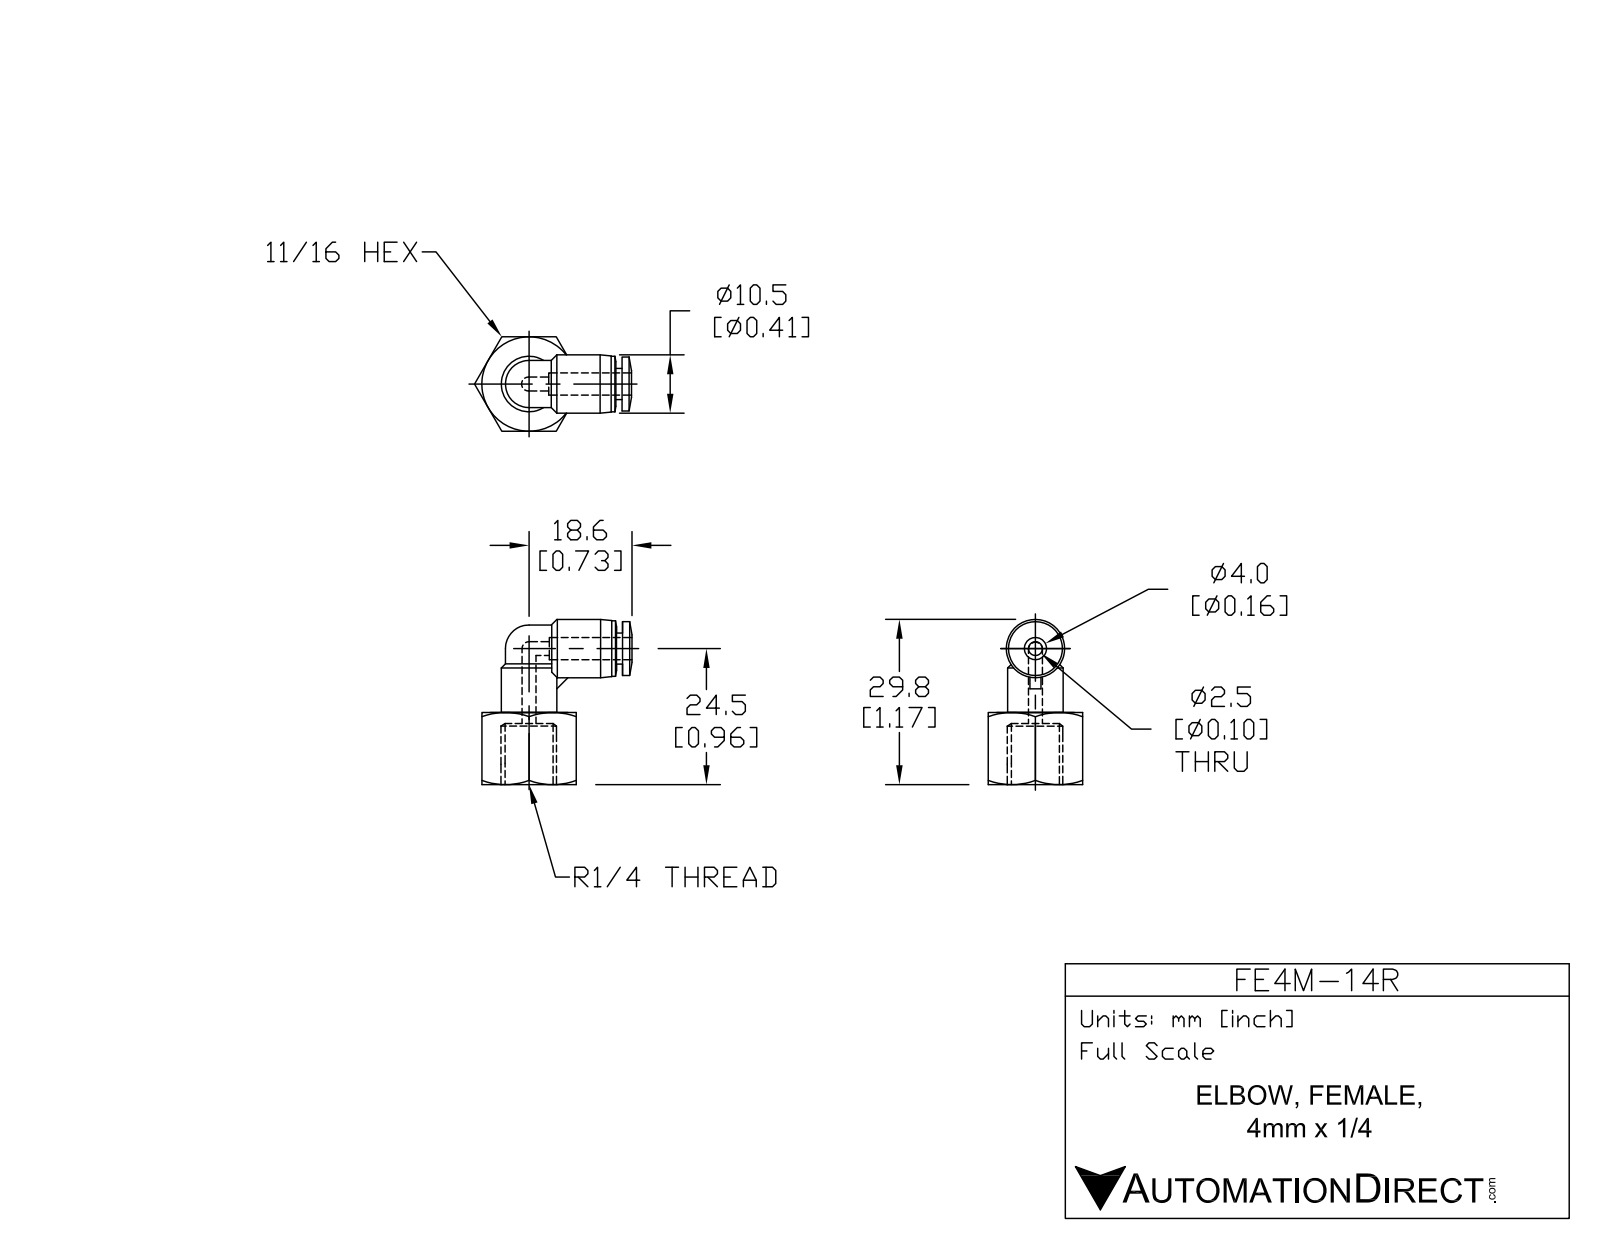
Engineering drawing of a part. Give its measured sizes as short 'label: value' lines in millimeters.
name: FE4M-14R
written by: SolidWorks 2015 (AUTOMOTIVE_DESIGN)
unit: mm
bodies: 1 solid, 67 faces (17 planar, 19 cylindrical, 31 other)
size: 29.7 × 28.3 × 17
volume: 3 640 mm³; area: 2 997 mm²
holes: 2× ⌀3, 1× ⌀4.3
bosses: 2× ⌀10, 1× ⌀10.5, 1× ⌀9.7, 1× ⌀5.6
rounds: 2× R4.2
face distances: 17, 2, 11, 13, 1.1, 12, 13.1, 7.5, 9.5, 11.2
